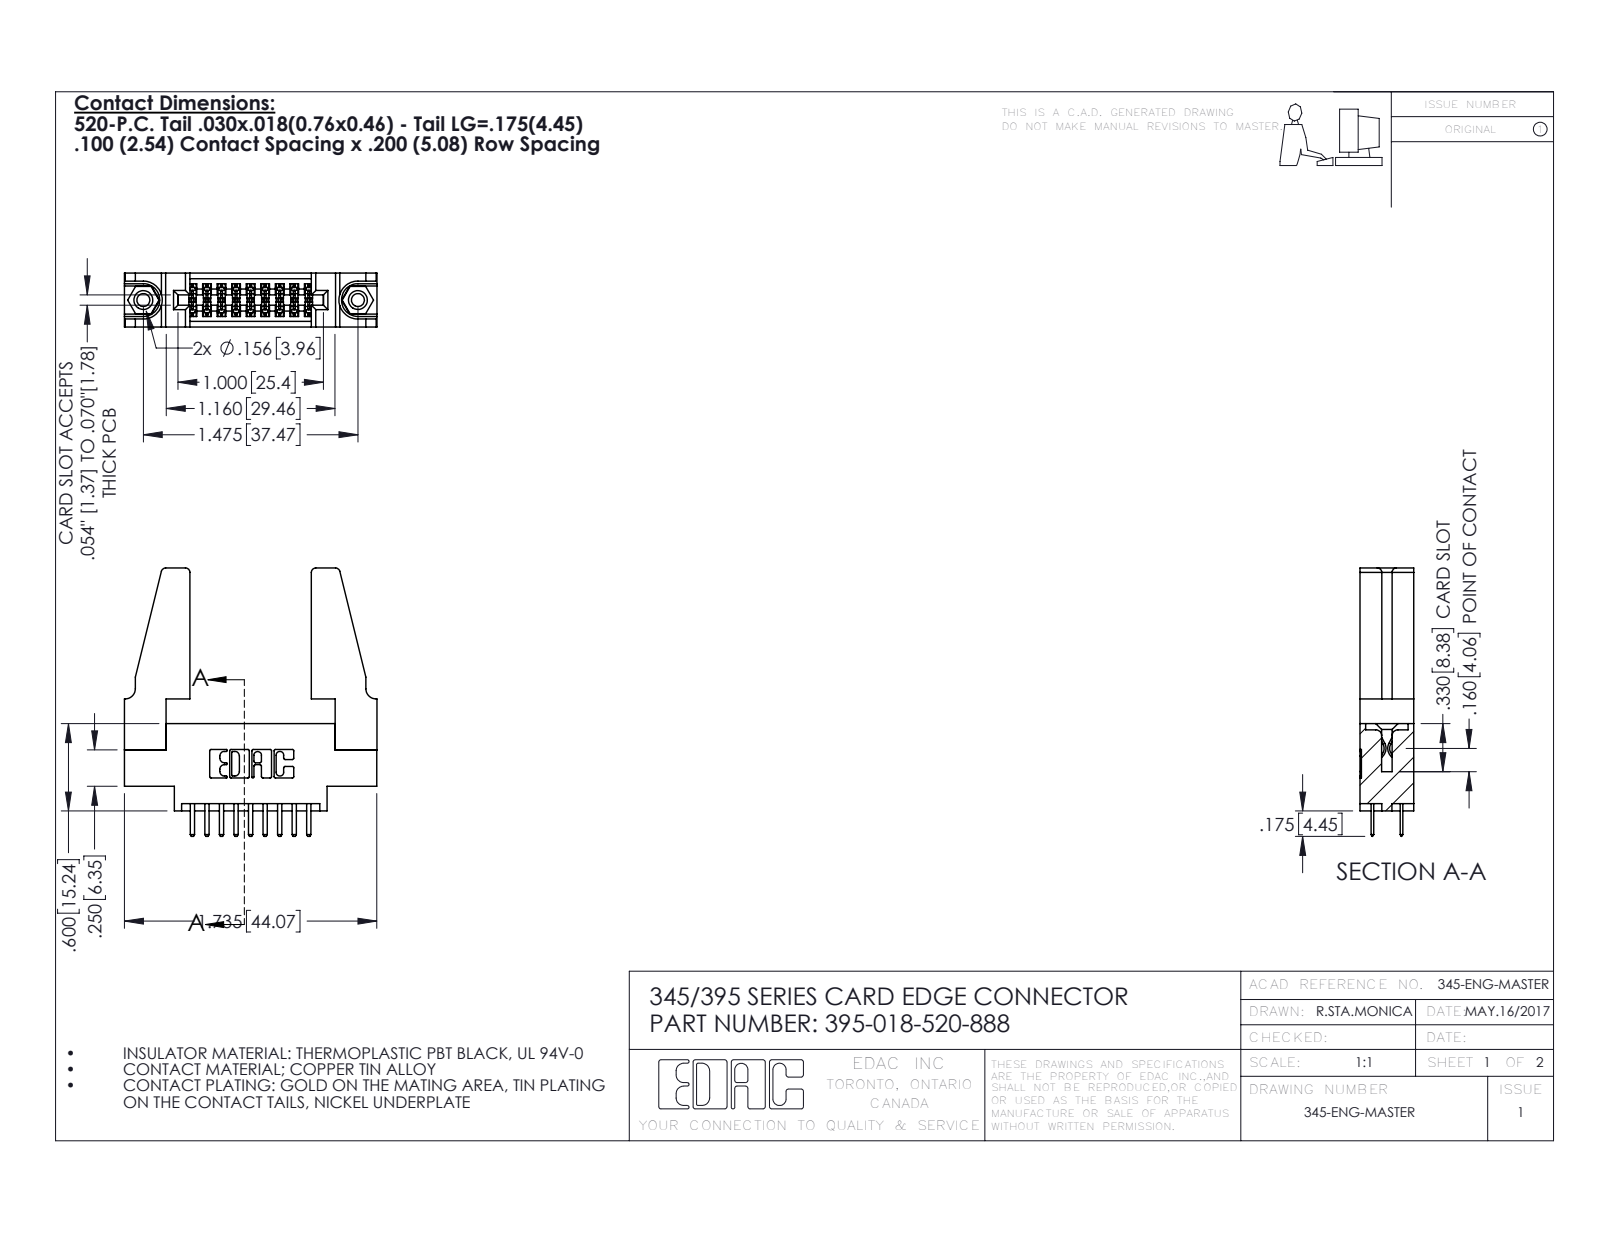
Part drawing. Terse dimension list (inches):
name: 345-292-001_345-293-120; 395-018-520-888; 345 Part_0.170 Offset - 0.156 Dia-TH; 345-250-001_345-250-001-102 (+1 more)
written by: SolidWorks 2016 (CONFIG_CONTROL_DESIGN)
unit: in
bodies: 23 solids, 1226 faces (786 planar, 424 cylindrical, 16 other)
size: 1.845 × 1.736 × 0.37
volume: 0.434 in³; area: 12.88 in²
holes: 2× ⌀0.089, 2× ⌀0.125, 2× ⌀0.156, 1× ⌀0.064
bosses: 2× ⌀0.155
rounds: 27× R0.006, 22× R0.01, 22× R0.01, 8× R0.03, 6× R0.007, 6× R0.031, 3× R0.026, 2× R0.014
face distances: 0.37, 0.072, 0.298, 0.2, 0.225, 0.098, 0.272, 0.025, 0.148, 0.15
hole spacings: 0.27, 1.244, 1.475
